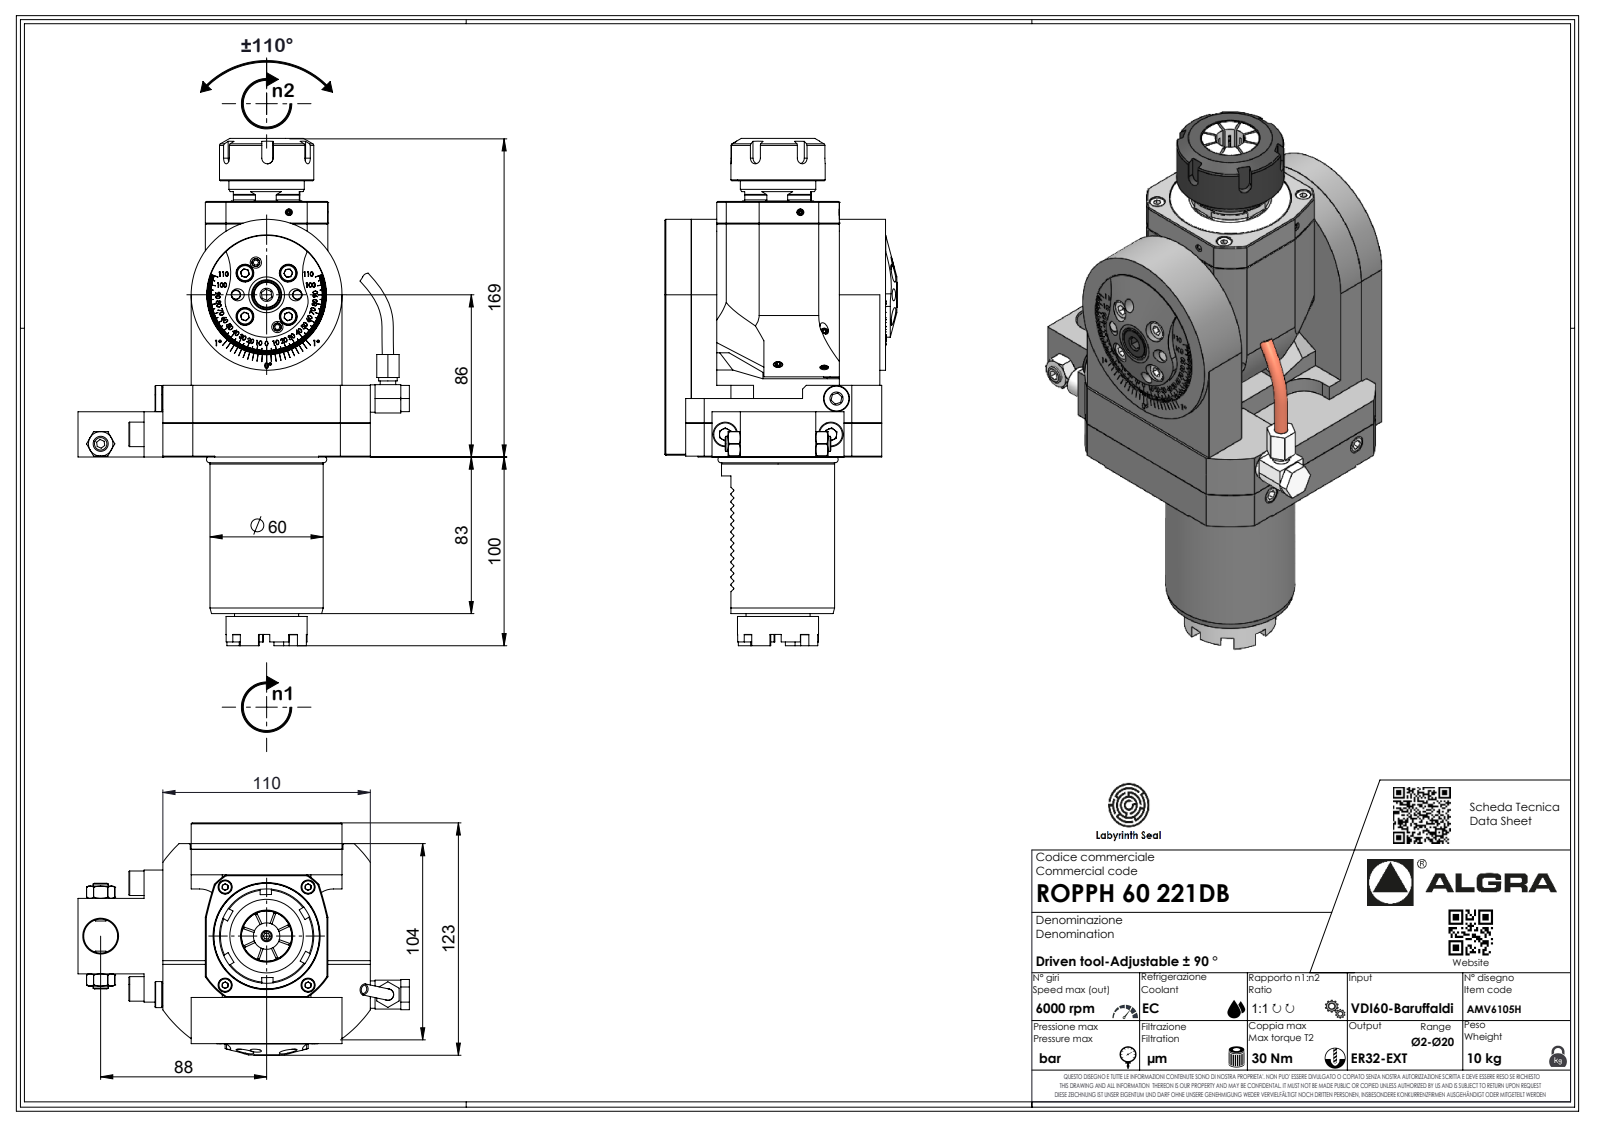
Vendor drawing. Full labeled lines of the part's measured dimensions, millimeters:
Part name (STEP PRODUCT): ROPPH60221DB
STEP written by: SolidWorks 2023 (AUTOMOTIVE_DESIGN)
Units: millimetres
Bodies: 1 solid, 661 faces (434 planar, 115 cylindrical, 112 other)
Overall size (bounding box): 268.91 × 175.7 × 123
Volume: 1 468 000 mm³ · Surface area: 125 873 mm²
Round holes (diameter × count): ⌀2.1 ×1
Round bosses / shafts (diameter × count): ⌀80 ×1, ⌀60 ×1, ⌀58.7 ×1, ⌀50 ×1, ⌀43 ×1, ⌀40 ×1, ⌀34 ×1, ⌀14.5 ×1
Partial cylindrical surfaces — rounded edges, fillets, slot ends (radius × count): R0.2 ×19, R0.3 ×14, R0.33 ×7, R0.52 ×7, R3.7 ×7, R3 ×5, R10 ×2, R12 ×2
Main face-to-face distances: 22.5, 87.5, 65, 80, 7.5, 95, 7, 15, 27.5, 72.5
